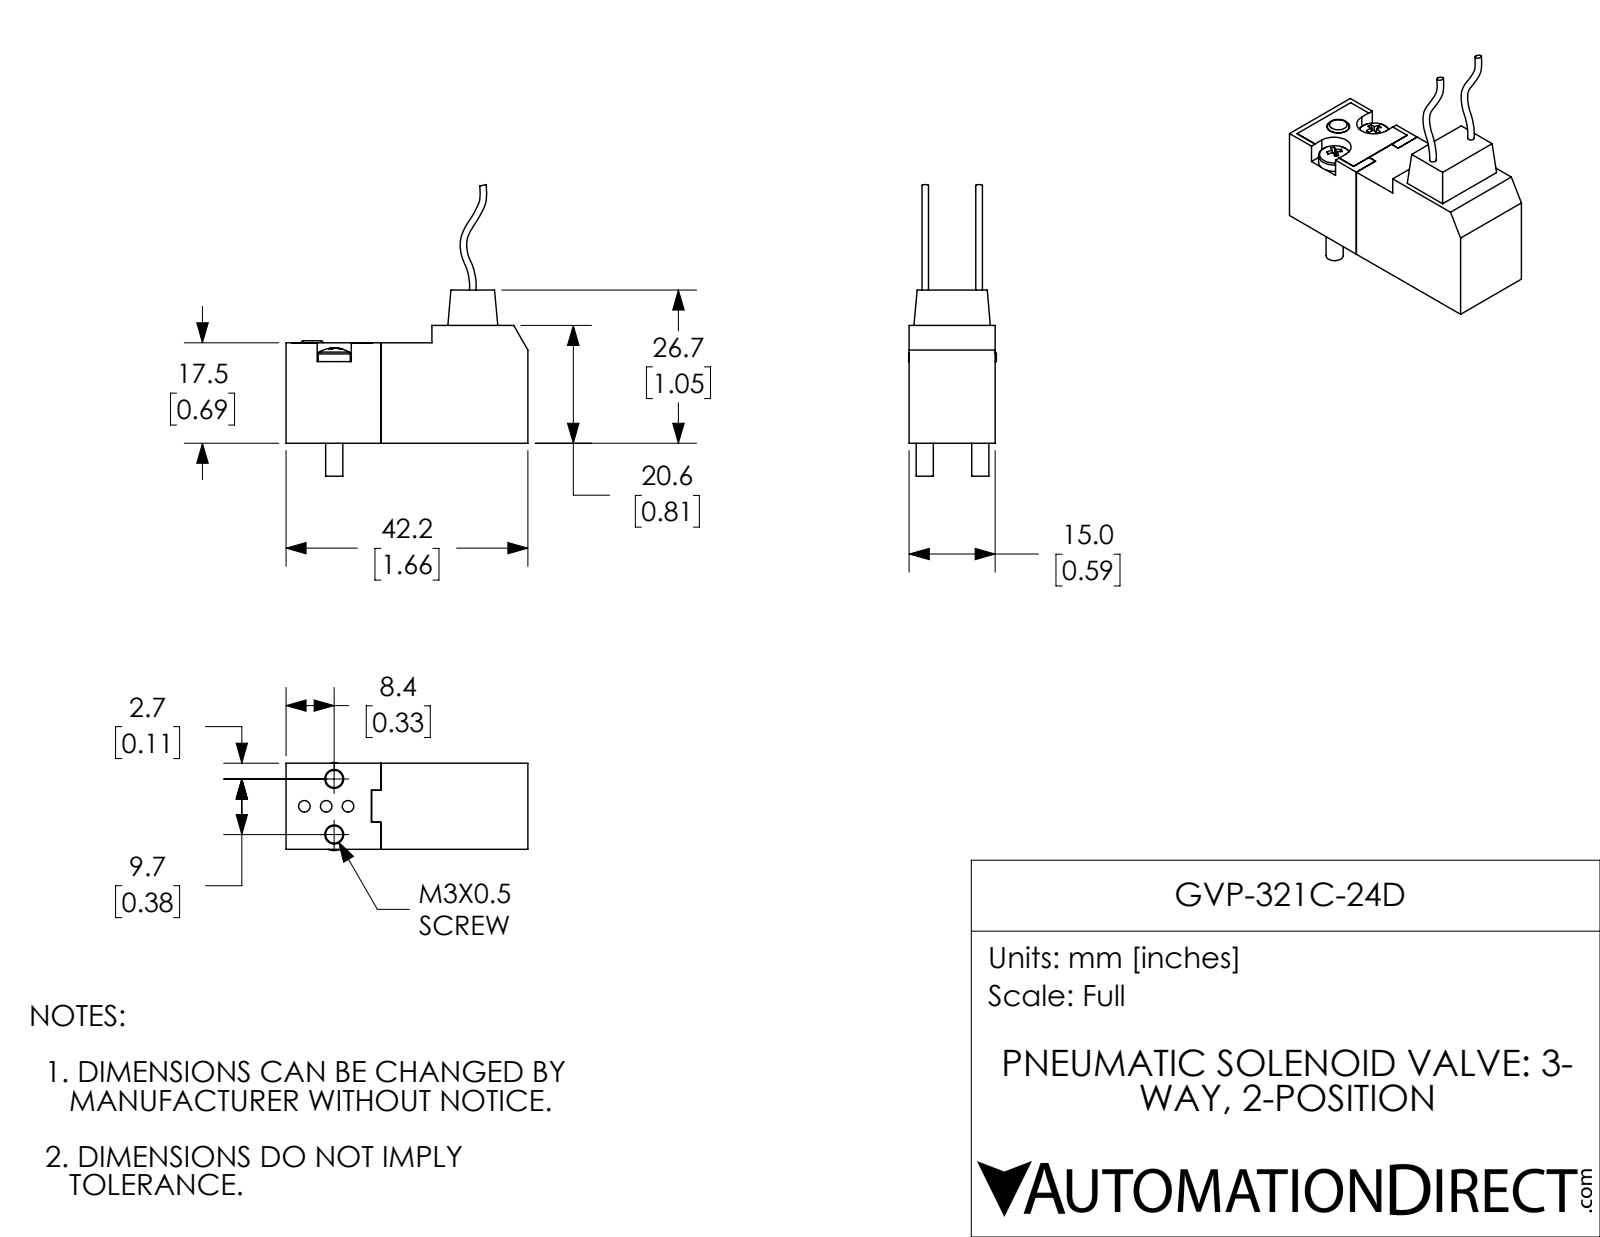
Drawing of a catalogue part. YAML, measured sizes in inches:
part_name: "GVP-321C-24D"
step_written_by: "SolidWorks 2018 (AUTOMOTIVE_DESIGN)"
units: inches
bodies: {solids: 4, faces: 116, planar: 79, cylindrical: 23, other: 14}
overall_size: [2.004, 1.663, 0.602]
volume: 0.755
surface_area: 8.426
round_holes:
  - {diameter: 0.079, count: 3}
  - {diameter: 0.13, count: 2}
  - {diameter: 0.155, count: 1}
round_bosses_or_shafts:
  - {diameter: 0.22, count: 2}
  - {diameter: 0.118, count: 2}
partial_cylinders:
  - {radius: 0.117, count: 2}
face_to_face_distances: [0.591, 0.651, 1.012, 1.663, 1.075, 0.063, 0.588, 0.69, 0.691, 0.186]
hole_center_spacings: [0.15, 0.053, 0.097, 0.196, 0.202, 0.211, 0.216, 0.242]
